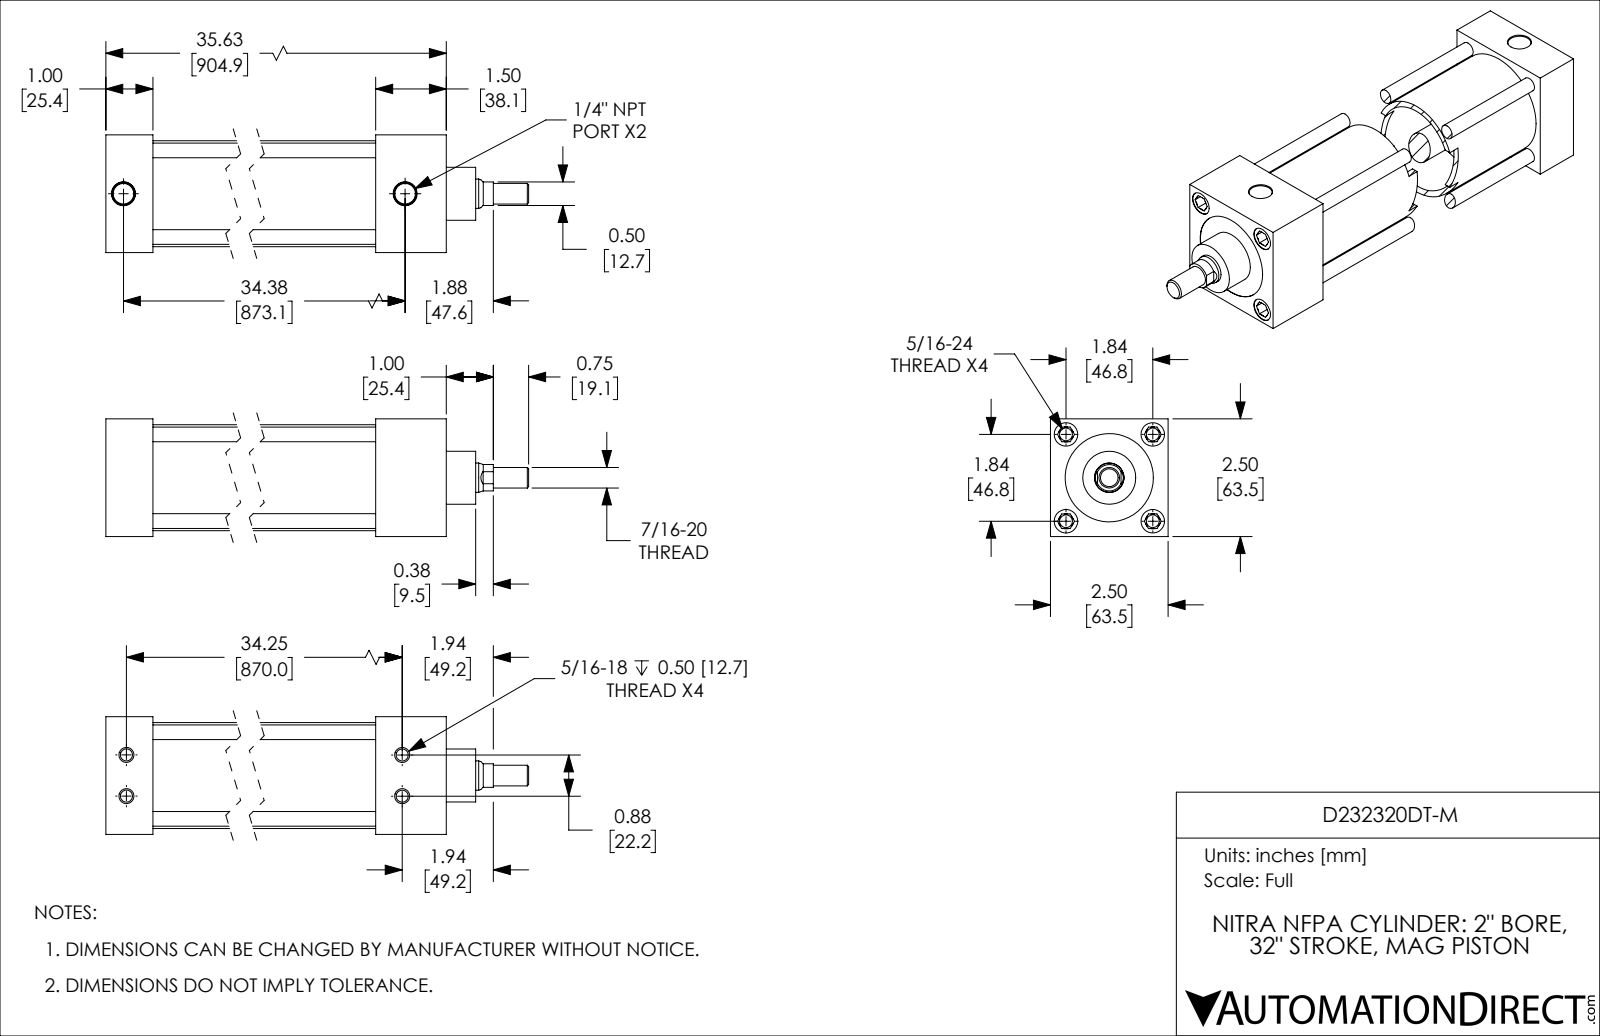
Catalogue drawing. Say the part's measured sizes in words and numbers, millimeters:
The part is named "D232320DT-M_PISTON_KK1; D232320DT-M; D232320DT-M_BODY". Its 3-D file was written by "SolidWorks 2019 (CONFIG_CONTROL_DESIGN)". It is 2 solids with 200 faces: 58 planar, 62 cylindrical and 80 other. Overall it measures 949.3 by 63.5 by 63.5 millimeters. Its volume is 1 094 000 cubic millimeters and its surface area 462 900 square millimeters. Round holes: 7 of diameter 6.9, 4 of diameter 6.5, 4 of diameter 12.7, 2 of diameter 11.1, 1 of diameter 15.9, 1 of diameter 47.6, 1 of diameter 50.8. Round bosses or shafts: 4 of diameter 7.9, 1 of diameter 57.2, 1 of diameter 50.8, 1 of diameter 28.6, 1 of diameter 15.8, 1 of diameter 11.1. Partial cylindrical surfaces (rounded edges, fillets, slot ends): 1 of radius 7.1. The main face-to-face distances are 63.5, 25.4, 866.8, 841.4, 28.6, 54, 812.8, 904.9, 879.5, 850.9. The hole center spacings are 46.7, 46.8, 33, 11.2, 11.3, 22.2, 33.1, 66.1.
